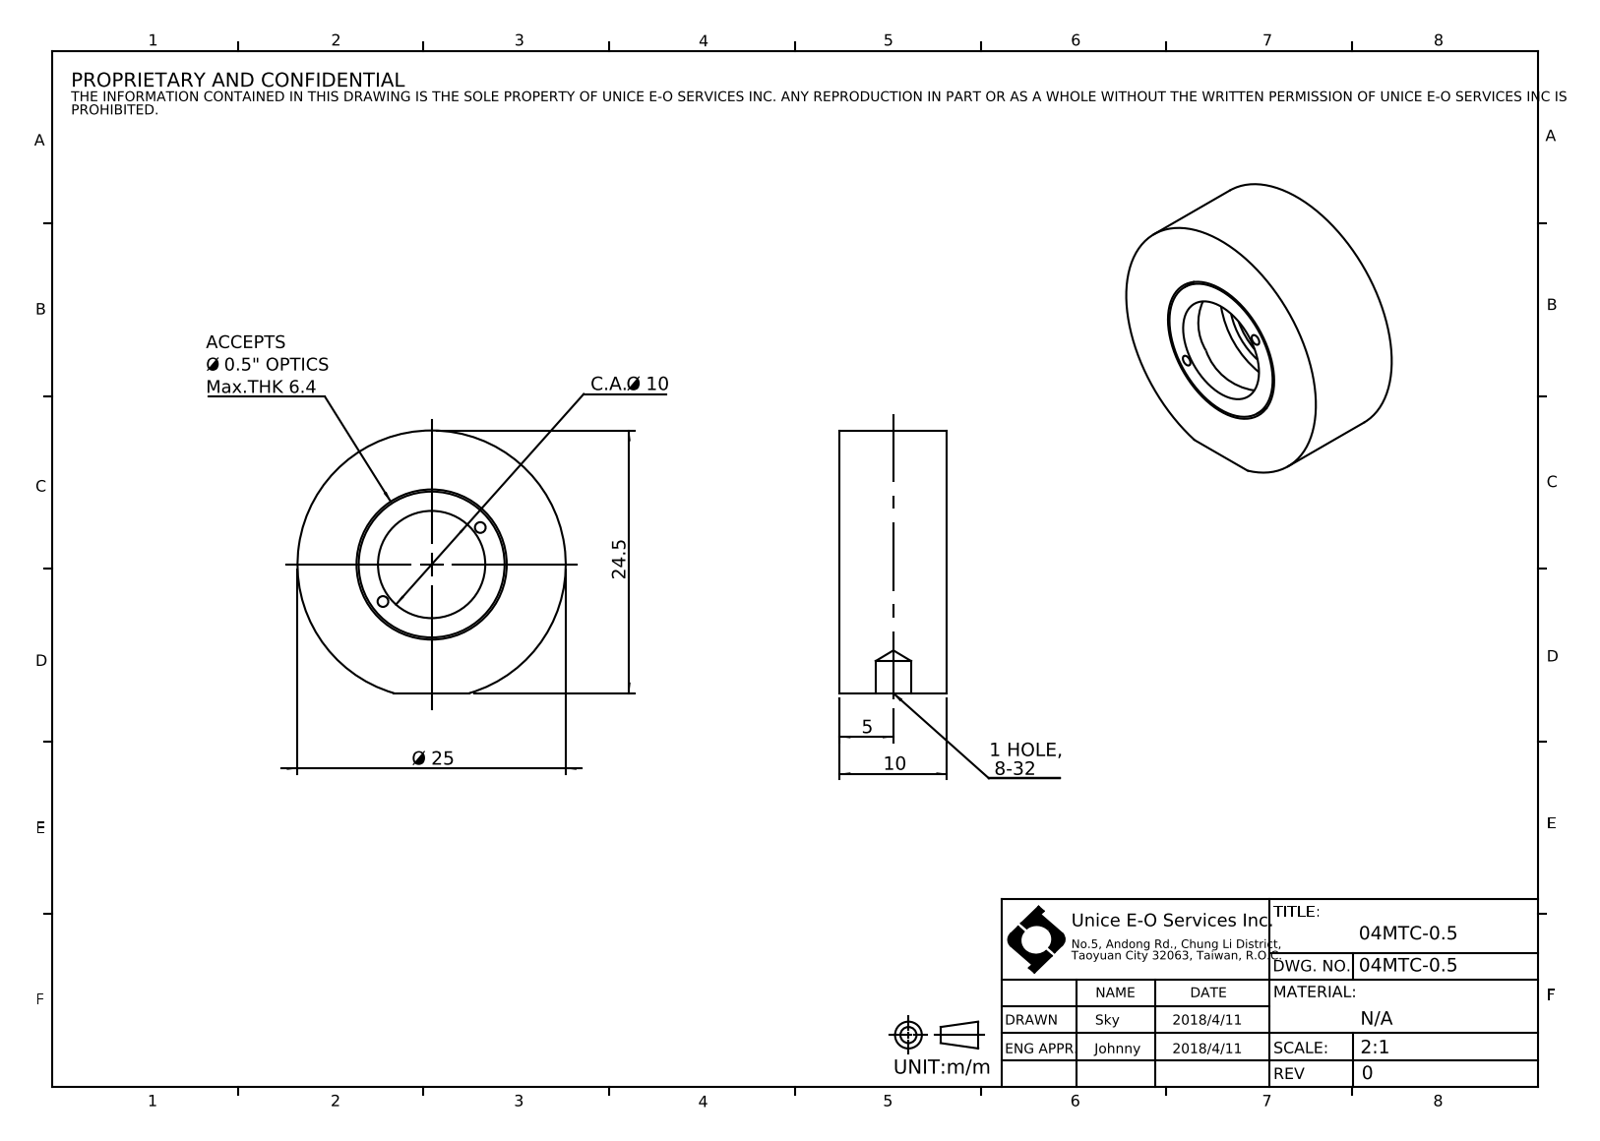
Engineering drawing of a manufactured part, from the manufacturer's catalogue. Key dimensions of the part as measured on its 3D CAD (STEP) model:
Part name (STEP PRODUCT): 04MTC-0.5
STEP written by: SolidWorks 2016 (CONFIG_CONTROL_DESIGN)
Units: millimetres
Bodies: 3 solids, 31 faces (8 planar, 21 cylindrical, 2 other)
Overall size (bounding box): 25 × 24.5 × 10
Volume: 3 538 mm³ · Surface area: 2 498 mm²
Round holes (diameter × count): ⌀1 ×2, ⌀3.45 ×1, ⌀10 ×1, ⌀14 ×1
Round bosses / shafts (diameter × count): ⌀25 ×1, ⌀13.6 ×1, ⌀12.5 ×1
Main face-to-face distances: 10, 1, 9, 8, 7, 2, 3.25, 3.85, 2.25, 2.85
Hole centre spacings: 5.69, 5.7, 11.4
